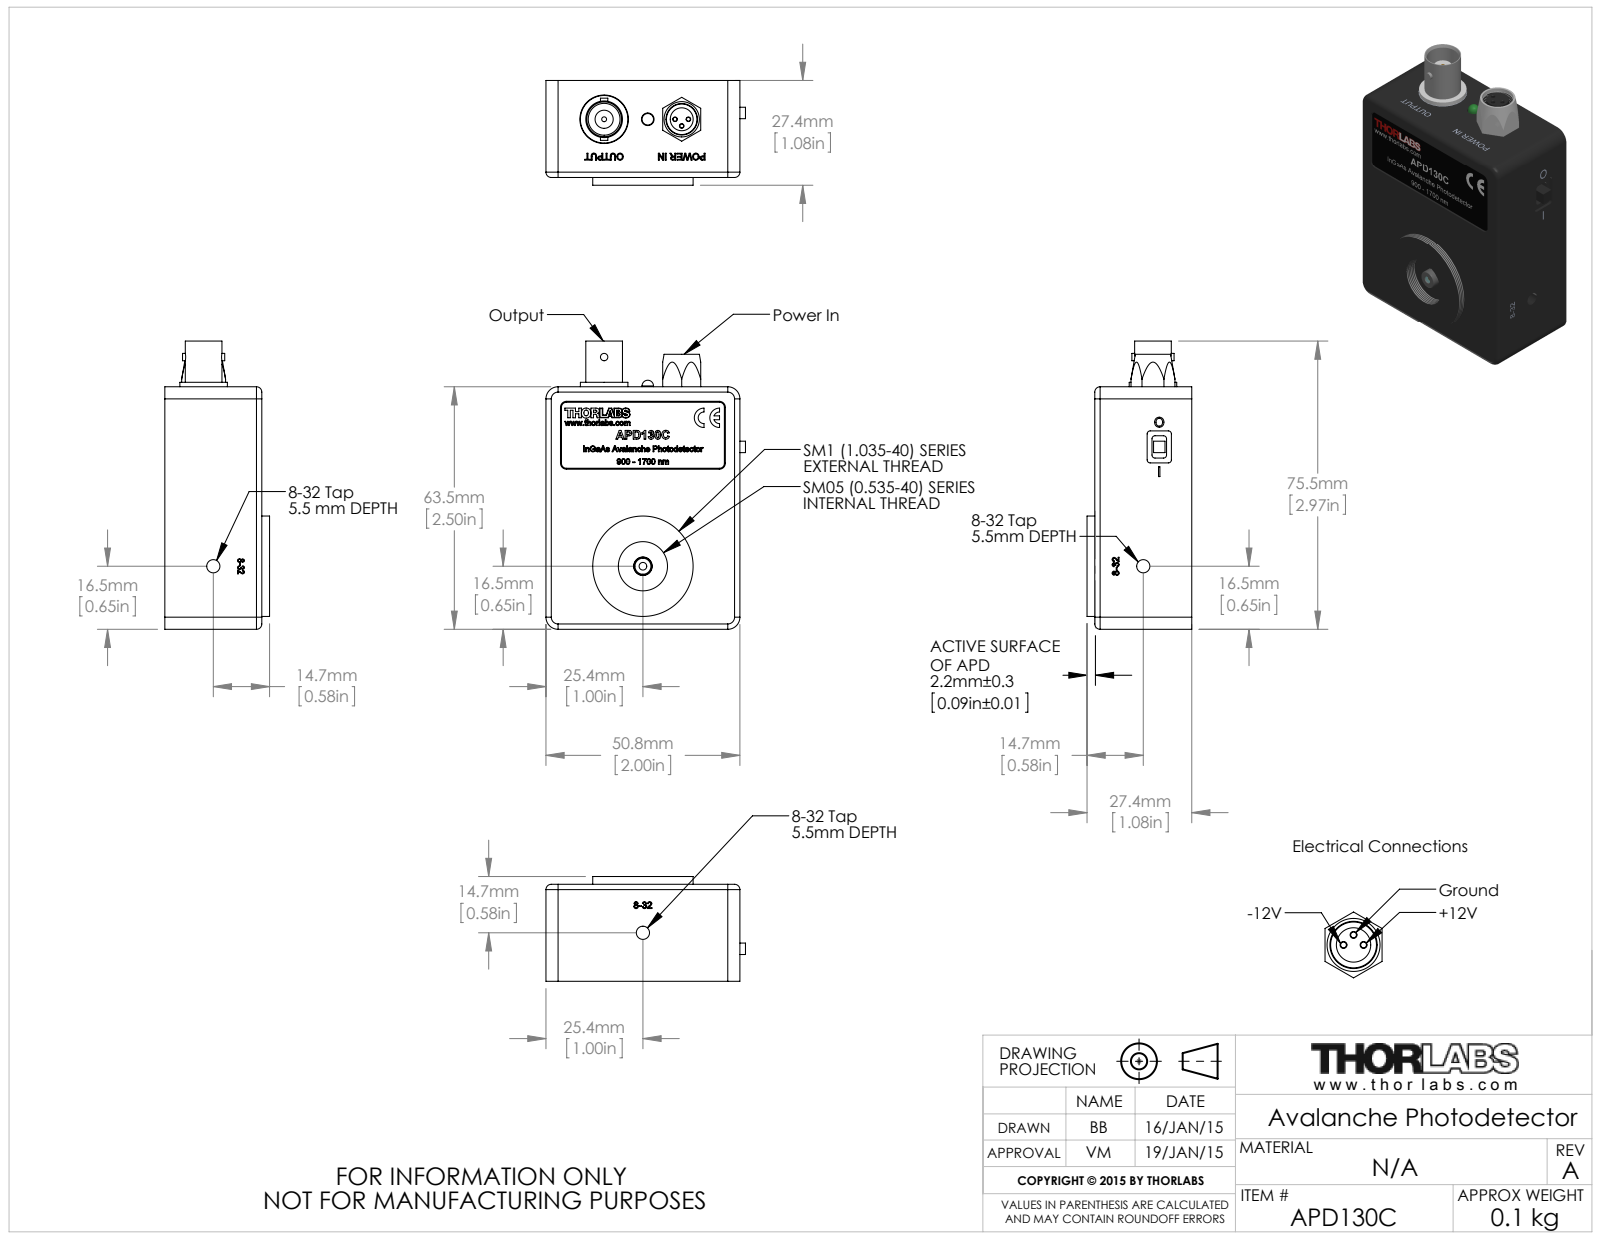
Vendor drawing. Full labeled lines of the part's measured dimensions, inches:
Part name (STEP PRODUCT): MTN004763-E0W
STEP written by: SolidWorks 2014 (AUTOMOTIVE_DESIGN)
Units: inches
Bodies: 12 solids, 2016 faces (983 planar, 252 cylindrical, 781 other)
Overall size (bounding box): 2.971 × 2.057 × 1.08
Volume: 2.205 in³ · Surface area: 44.74 in²
Round holes (diameter × count): ⌀0.063 ×8, ⌀0.094 ×4, ⌀0.039 ×3, ⌀0.04 ×3, ⌀0.136 ×2, ⌀0.05 ×1, ⌀0.052 ×1, ⌀0.079 ×1, ⌀0.098 ×1, ⌀0.13 ×1, ⌀0.163 ×1, ⌀0.191 ×1
Round bosses / shafts (diameter × count): ⌀0.02 ×6, ⌀0.15 ×5, ⌀0.079 ×4, ⌀0.018 ×3, ⌀1.035 ×1, ⌀0.49 ×1, ⌀0.43 ×1, ⌀0.378 ×1
Partial cylindrical surfaces — rounded edges, fillets, slot ends (radius × count): R0.125 ×18, R0.13 ×14, R0.031 ×8, R0.075 ×8, R0.095 ×8, R0.1 ×5, R0.05 ×4, R0.055 ×4
Main face-to-face distances: 0.063, 0.1, 1, 0.937, 0.045, 0.02, 0.98, 0.917, 0.935, 0.872
Hole centre spacings: 0.174, 1.621, 2.013, 2.579, 0.05, 0.069, 0.071, 0.097
